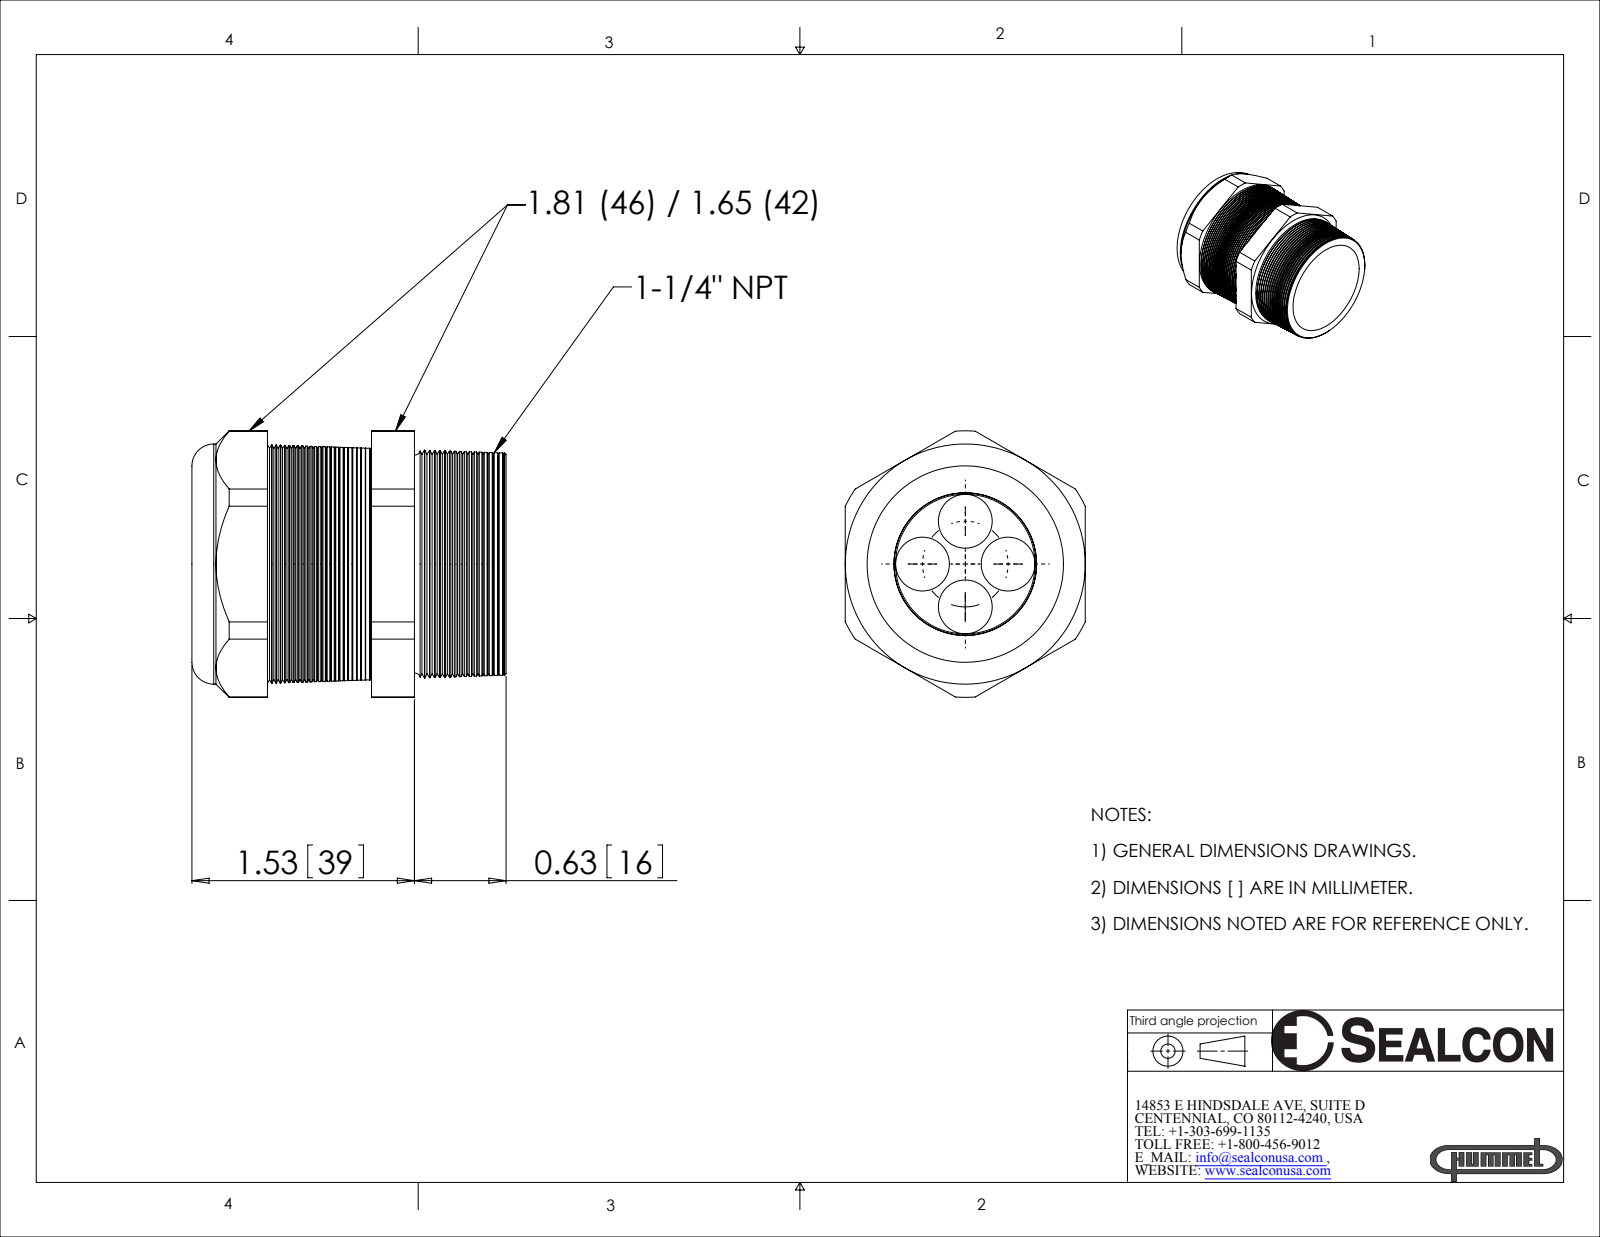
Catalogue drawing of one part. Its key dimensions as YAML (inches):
part_name: "CD29L3-BK"
step_written_by: "SolidWorks 2007 (CONFIG_CONTROL_DESIGN)"
units: inches
bodies: {solids: 2, faces: 315, planar: 21, cylindrical: 28, other: 266}
overall_size: [2.16, 1.831, 1.65]
volume: 2.548
surface_area: 29.67
round_holes:
  - {diameter: 0.37, count: 4}
  - {diameter: 0.96, count: 1}
  - {diameter: 0.98, count: 1}
round_bosses_or_shafts:
  - {diameter: 1.65, count: 1}
partial_cylinders:
  - {radius: 0.916, count: 1}
face_to_face_distances: [1.65, 1.65, 2.16, 1.235, 0.925, 0.5, 0.735, 1.66, 0.02, 0.48]
hole_center_spacings: [0.294, 0.416, 0.588]
